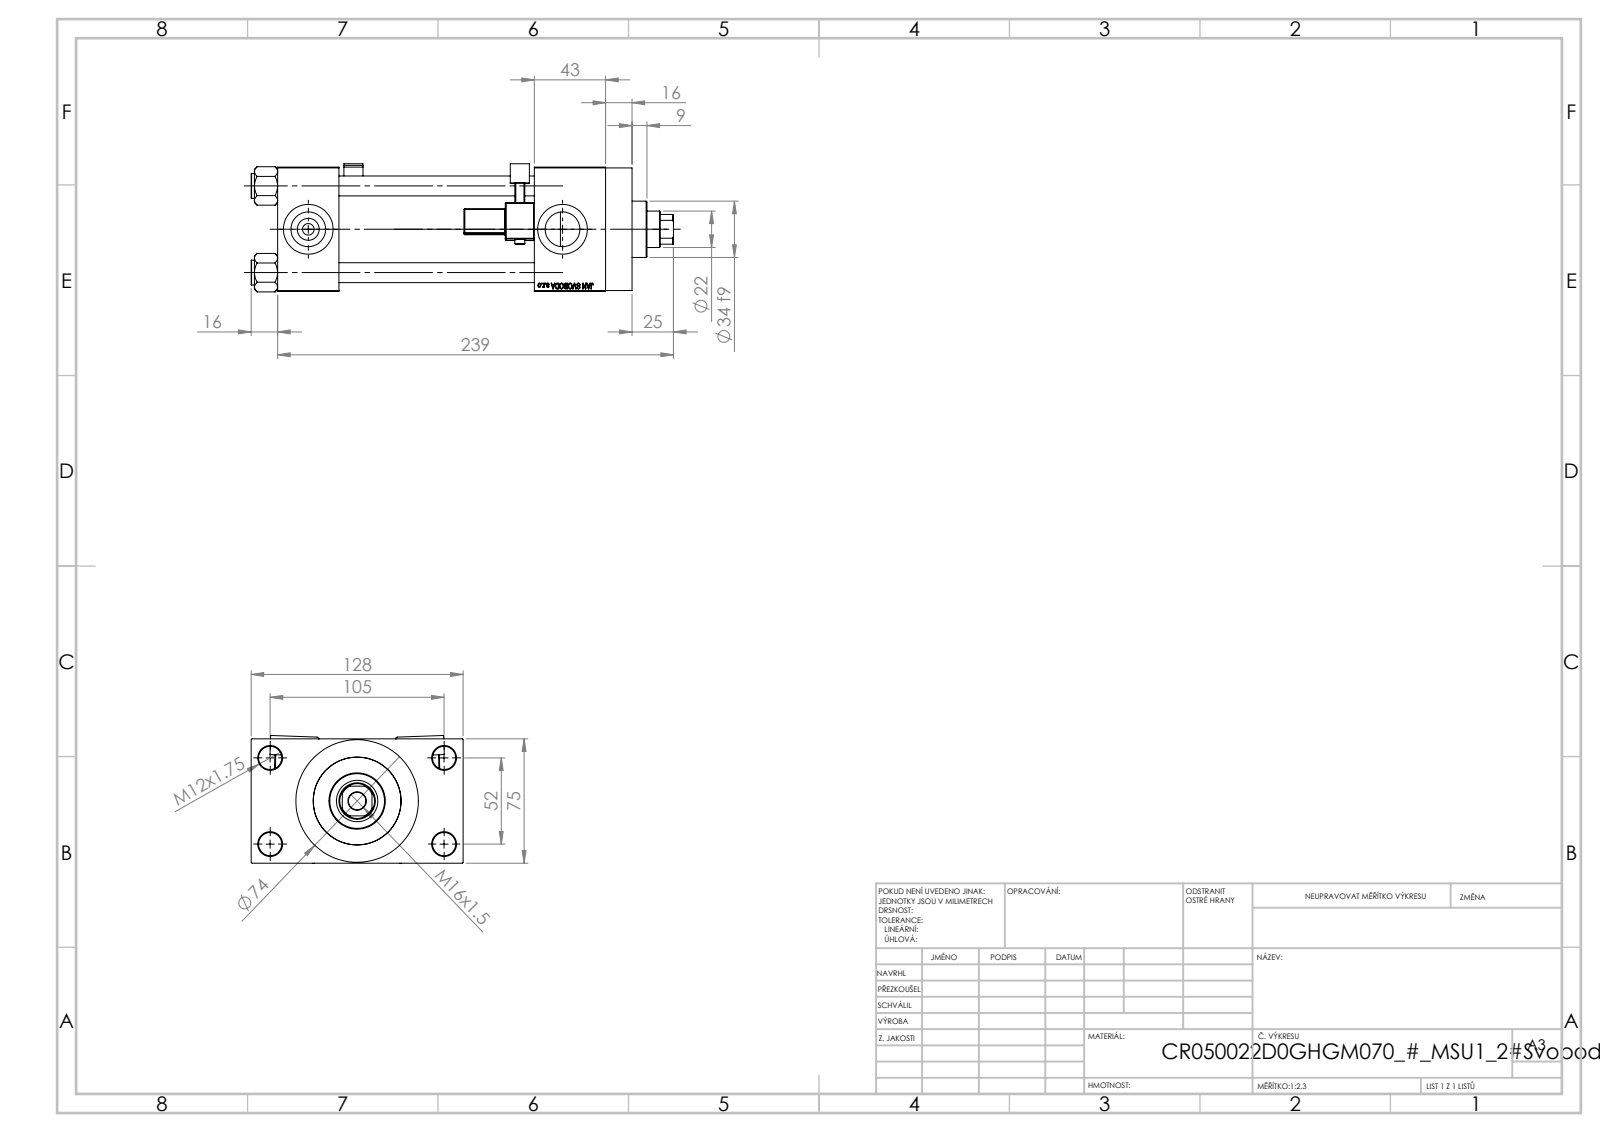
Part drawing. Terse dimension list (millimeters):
name: V215CR_VCP_D; V215CR_D_Body; V215_VC_A; NUT_M5_D (+2 more)
written by: SolidWorks 2019 (CONFIG_CONTROL_DESIGN)
unit: mm
bodies: 13 solids, 1257 faces (555 planar, 148 cylindrical, 554 other)
size: 255 × 128 × 77.3
volume: 918 587 mm³; area: 212 131 mm²
holes: 4× ⌀12, 4× ⌀14, 2× ⌀7, 2× ⌀20.96, 2× ⌀30, 1× ⌀10.5, 1× ⌀22, 1× ⌀25, 1× ⌀41, 1× ⌀50, 1× ⌀53
bosses: 4× ⌀15, 2× ⌀6, 1× ⌀74, 1× ⌀56, 1× ⌀34
rounds: 48× R0.5, 2× R1, 2× R2.5, 2× R4, 1× R10.5
face distances: 75, 118, 37, 155, 26.5, 101.5, 198, 161, 43, 16
hole spacings: 26.35, 36.98, 52.3, 58.43, 58.59, 78.65, 94.37, 52
